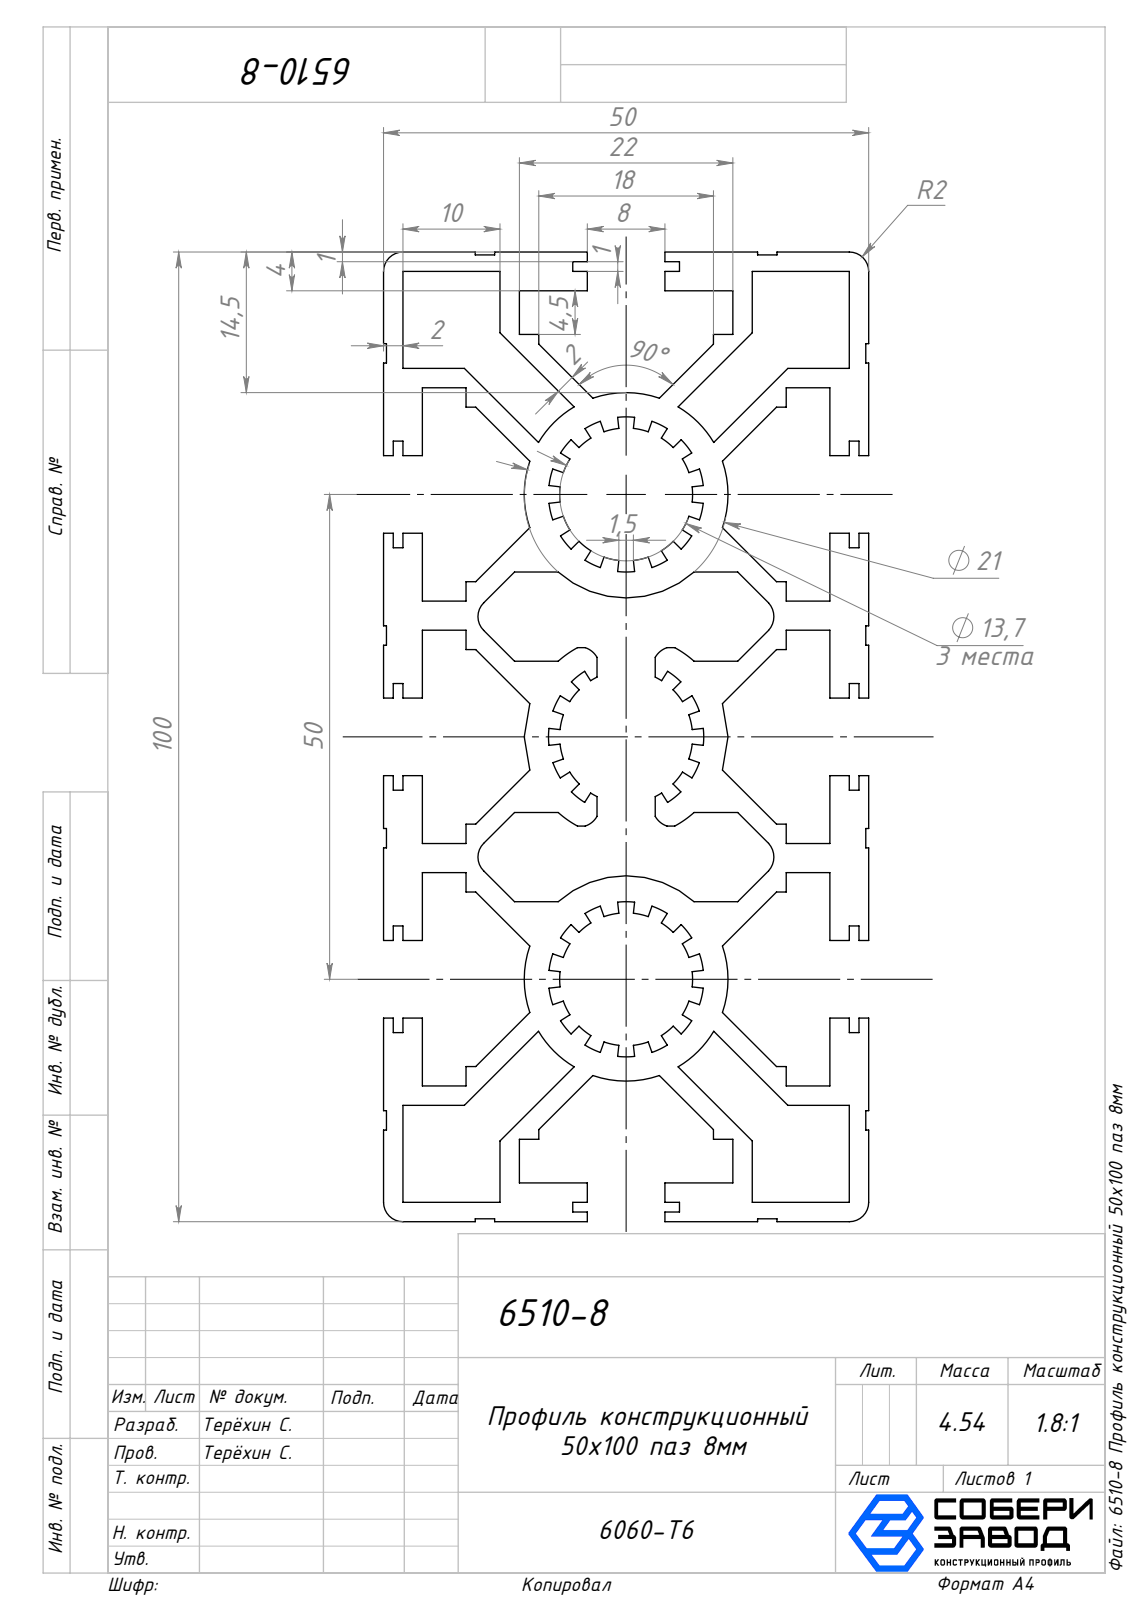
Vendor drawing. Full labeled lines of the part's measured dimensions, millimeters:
Part name (STEP PRODUCT): 6510-8 Профиль конструкционный 50х100 паз 8мм; 6510-8 Профиль конструкционный 50х100 паз 8мм_00
STEP written by: SolidWorks 2026 (CONFIG_CONTROL_DESIGN)
Units: millimetres
Bodies: 1 solid, 460 faces (346 planar, 114 cylindrical, 0 other)
Overall size (bounding box): 1000 × 100 × 50
Volume: 1 683 000 mm³ · Surface area: 1 364 000 mm²
Partial cylindrical surfaces — rounded edges, fillets, slot ends (radius × count): R10.5 ×7, R2 ×6, R2.2 ×4, R6.85 ×3, R8 ×3, R2.11 ×2
Main face-to-face distances: 2, 46, 4, 10, 12, 50, 7.2, 35.35, 8, 34
